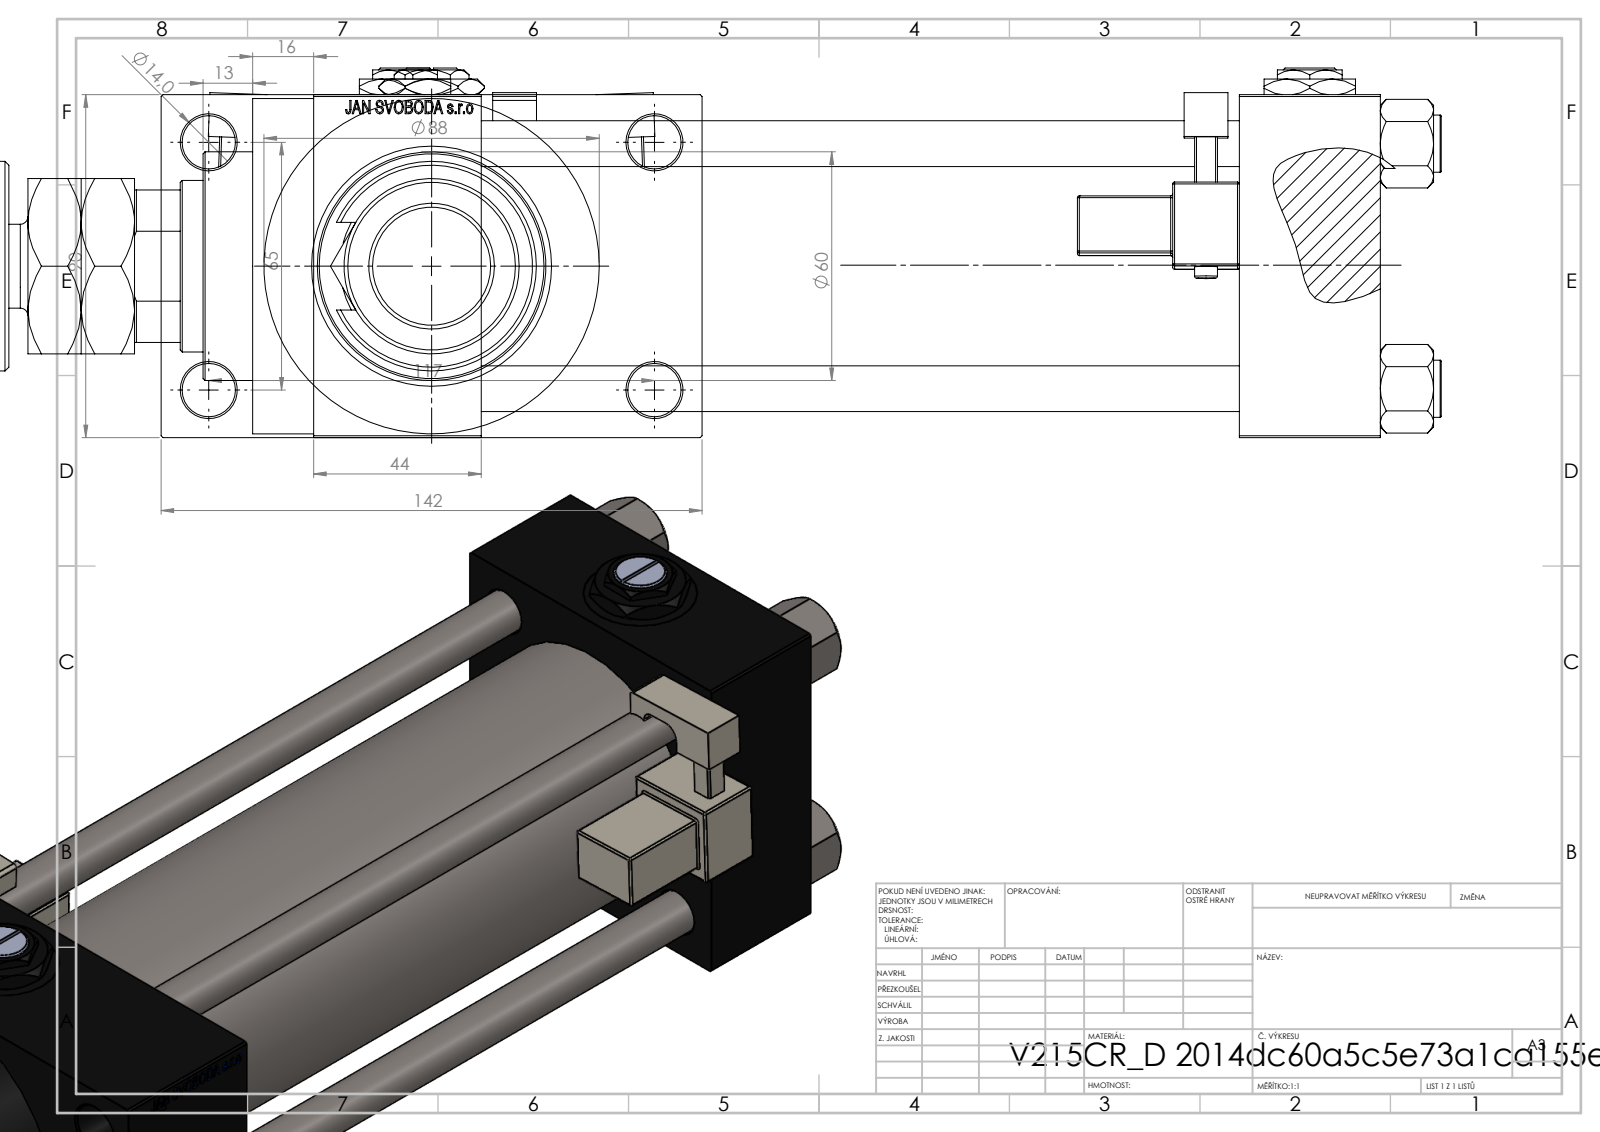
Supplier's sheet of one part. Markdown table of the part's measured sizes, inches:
| quantity | value |
| --- | --- |
| part name | MFA; FEMALE_PART_FOR_DFA; V215CR_D_Body; V215CR_VCP_D (+5 more) |
| STEP written by | SolidWorks 2019 (CONFIG_CONTROL_DESIGN) |
| units | inches |
| bodies | 17 solids, 1442 faces (630 planar, 170 cylindrical, 642 other) |
| overall size | 18.307 × 5.591 × 3.819 |
| volume | 105.6 in³ |
| surface area | 556.4 in² |
| round holes (diameter × count) | 0.472 × 4, 0.551 × 4, 0.825 × 4, 1.181 × 4, 0.276 × 3, 1.24 × 1, 1.535 × 1, 1.772 × 1, 1.89 × 1, 1.969 × 1, 2.362 × 1, 2.48 × 1 |
| round bosses / shafts (diameter × count) | 0.591 × 4, 0.236 × 2, 3.465 × 1, 2.717 × 1, 2.165 × 1, 1.811 × 1, 1.378 × 1, 1.299 × 1 |
| partial cylindrical surfaces (radius × count) | 0.02 × 48, 0.039 × 2, 0.098 × 2, 0.157 × 2, 0.453 × 1, 0.866 × 1 |
| main face-to-face distances | 3.543, 7.835, 1.457, 9.291, 1.024, 1.732, 11.024, 9.567, 4.567, 0.63 |
| hole center spacings | 1.037, 1.79, 2.531, 2.635, 2.748, 3.569, 4.383, 2.559 |
